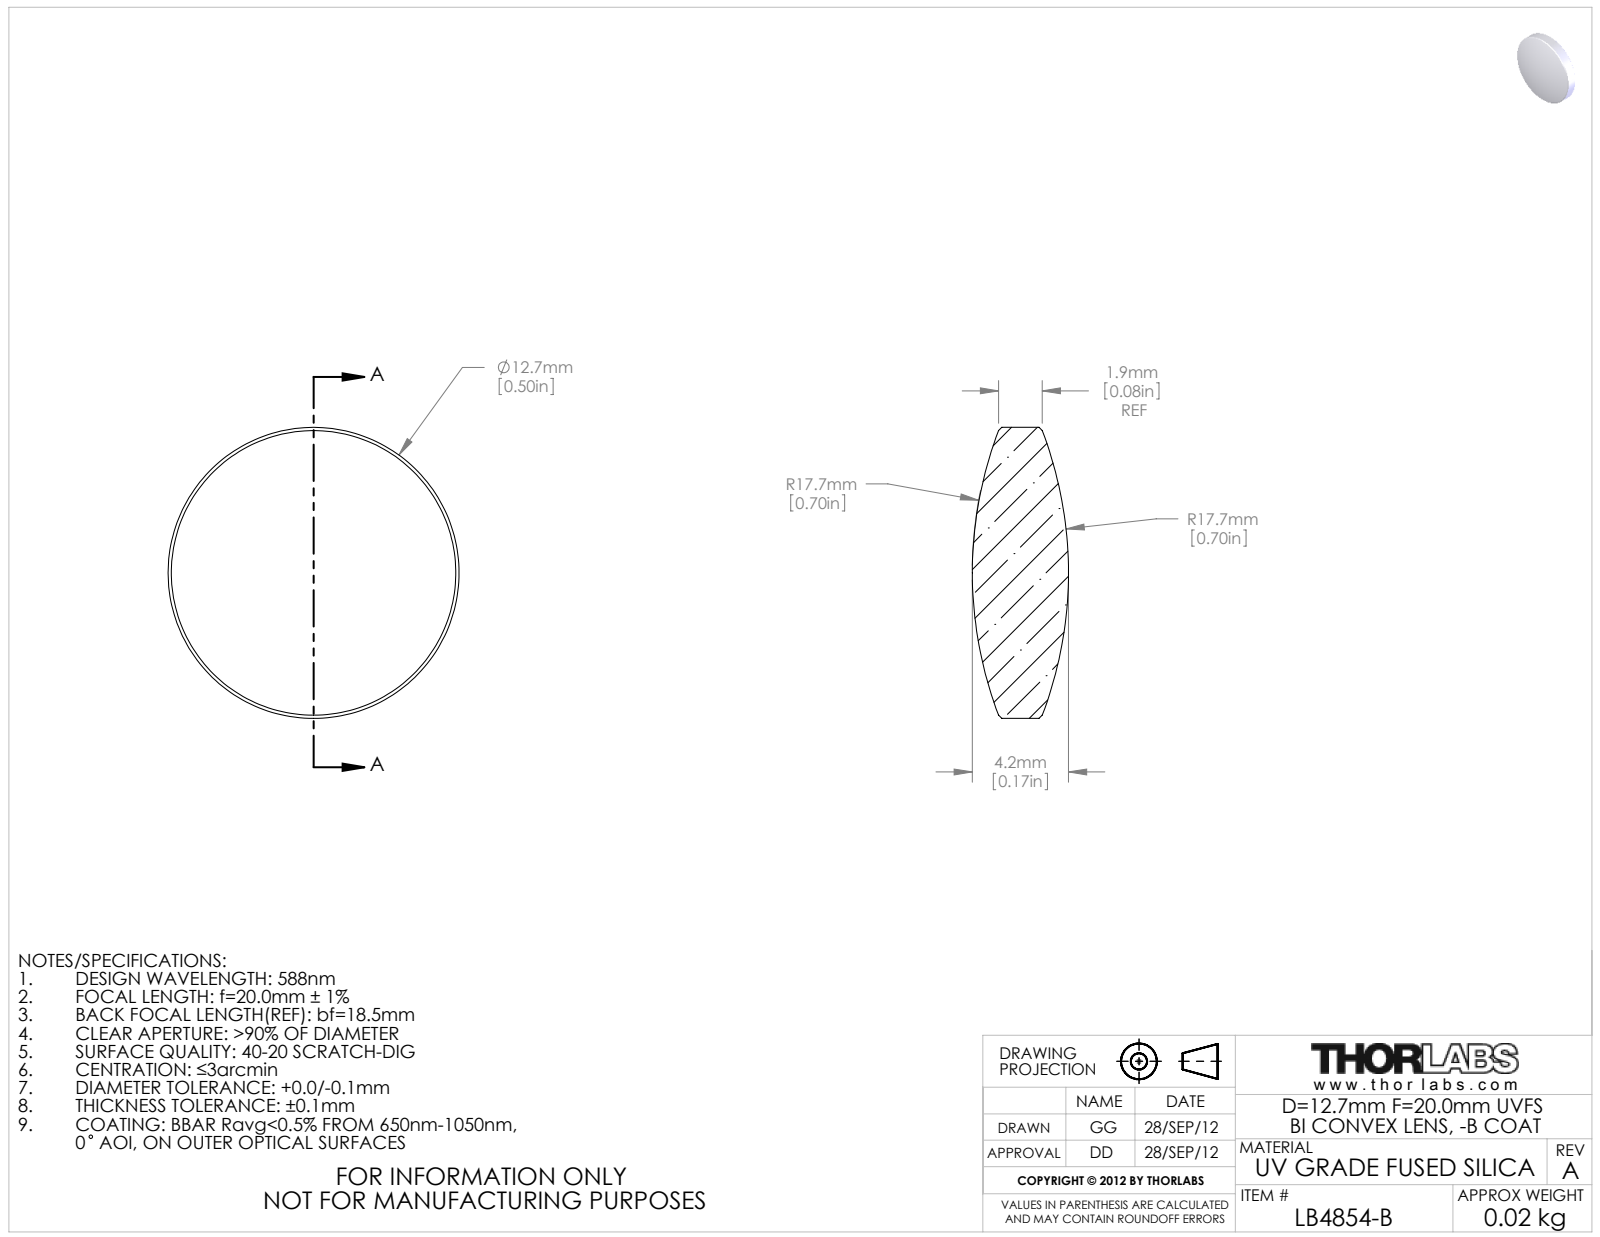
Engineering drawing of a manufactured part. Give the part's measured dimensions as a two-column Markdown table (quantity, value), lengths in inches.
| quantity | value |
| --- | --- |
| part name | 25009-E0W |
| STEP written by | SolidWorks 2011 (CONFIG_CONTROL_DESIGN) |
| units | inches |
| bodies | 1 solid, 10 faces (0 planar, 2 cylindrical, 8 other) |
| overall size | 0.5 × 0.5 × 0.165 |
| volume | 0.023 in³ |
| surface area | 0.513 in² |
| round bosses / shafts (diameter × count) | 0.5 × 1 |
